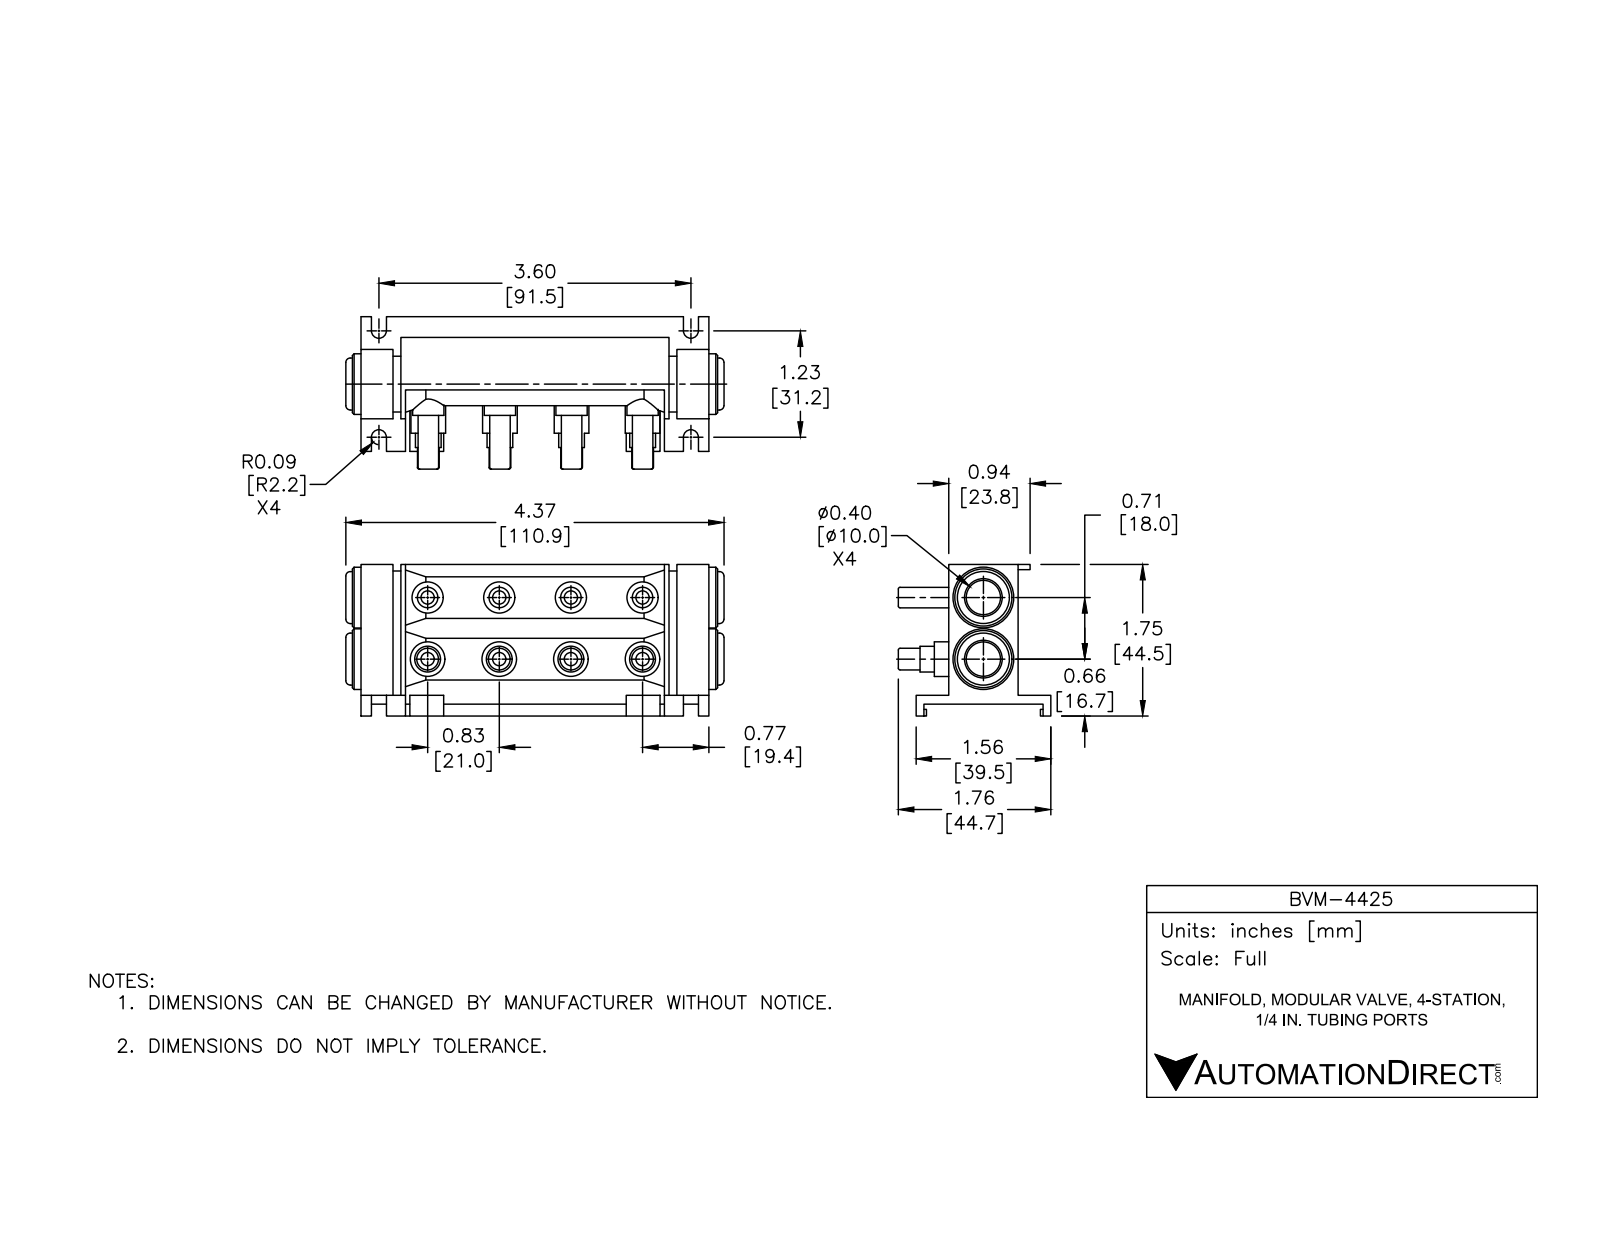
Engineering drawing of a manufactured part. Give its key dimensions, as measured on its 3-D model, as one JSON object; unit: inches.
{"part_name": "BVM-4425", "step_written_by": "SolidWorks 2016 (AUTOMOTIVE_DESIGN)", "units": "inches", "bodies": {"solids": 5, "faces": 316, "planar": 140, "cylindrical": 128, "other": 48}, "overall_size": [4.338, 1.759, 1.75], "volume_in3": 3.018, "surface_area_in2": 57.36, "round_holes": [[0.101, 8], [0.165, 8], [0.362, 2]], "round_bosses_or_shafts": [[0.25, 8], [0.4, 4], [0.361, 4], [0.297, 4], [0.7, 2], [0.6, 2], [0.5, 2]], "partial_cylinders_radius": [[0.086, 4]], "face_to_face_distances": [0.103, 0.332, 0.468, 1.613, 1.51, 3.988, 0.06, 1.553, 1.45, 0.136], "hole_center_spacings": [0.71, 0.827, 1.09, 0.827, 1.09, 1.654, 1.654, 1.8]}
